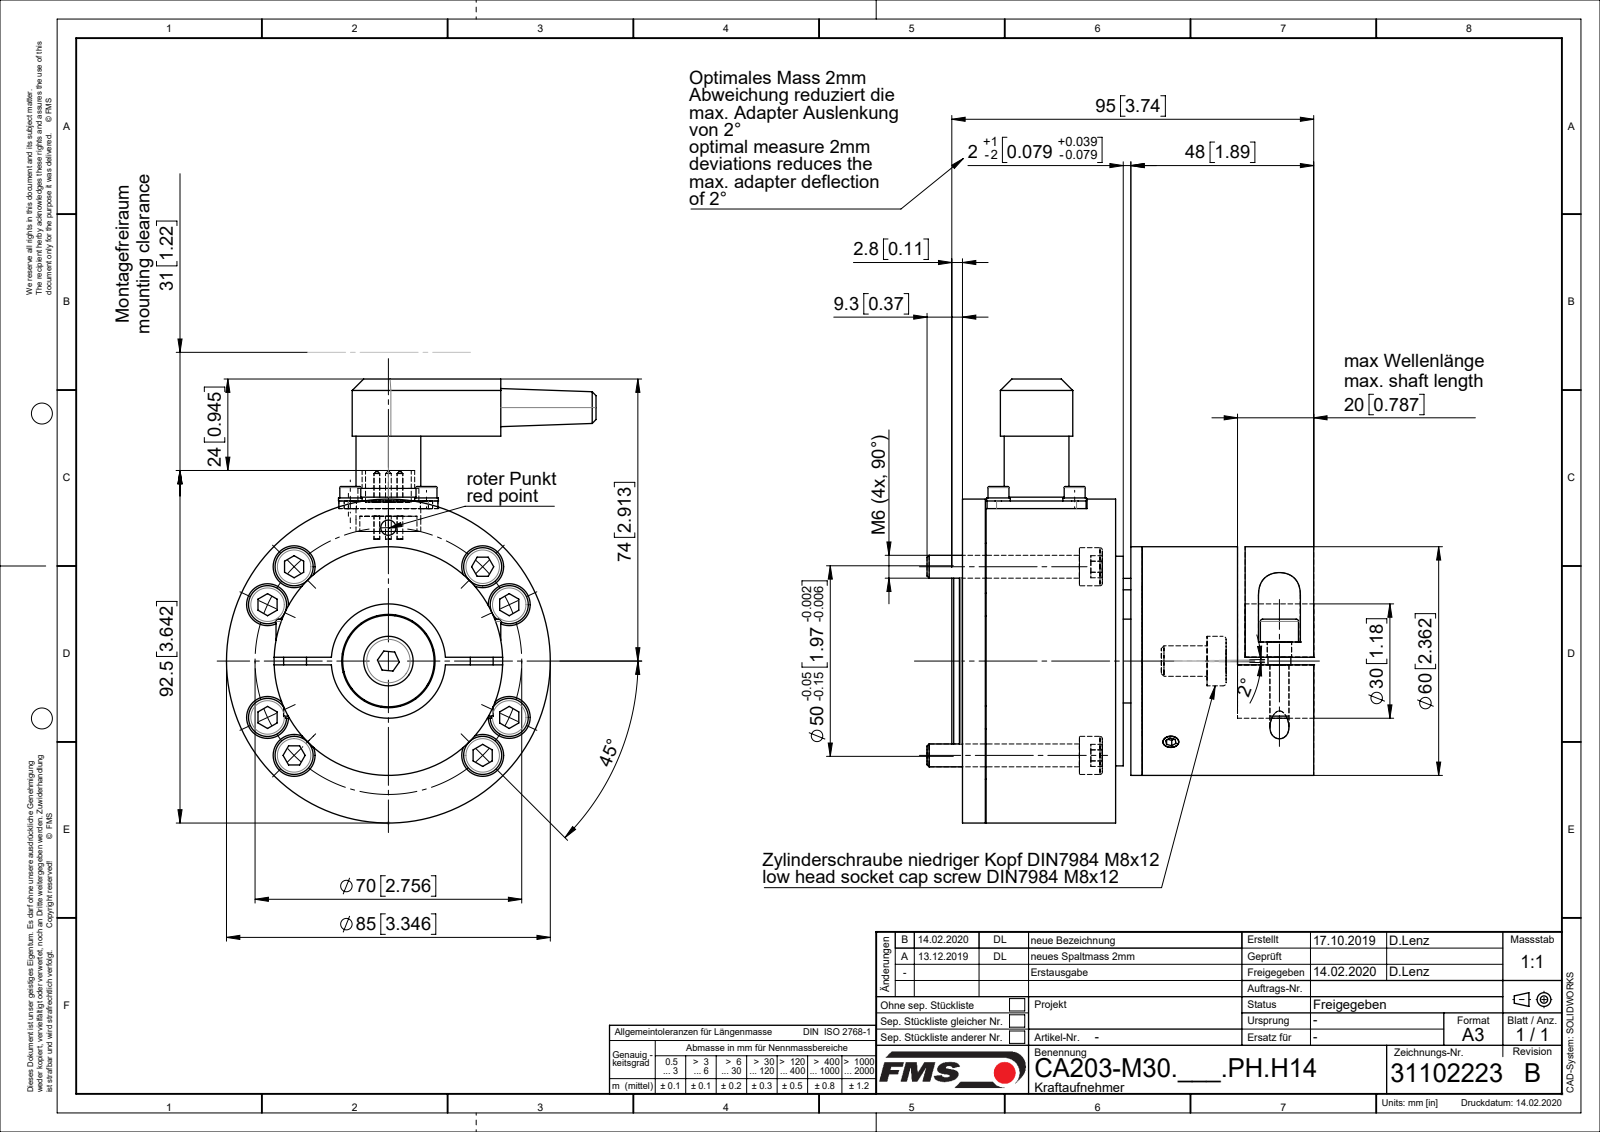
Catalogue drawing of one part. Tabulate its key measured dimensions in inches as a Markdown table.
| quantity | value |
| --- | --- |
| part name | ZEICHNUNG6; C50417_DM30; C0709081; C0612056 (+8 more) |
| STEP written by | Mechanical Desktop 2009 (CONFIG_CONTROL_DESIGN) |
| units | inches |
| bodies | 38 solids, 758 faces (274 planar, 331 cylindrical, 153 other) |
| overall size | 4.587 × 3.976 × 3.819 |
| volume | 18.04 in³ |
| surface area | 171.5 in² |
| round holes (diameter × count) | 0.102 × 8, 0.256 × 8, 0.433 × 8, 0.203 × 6, 0.079 × 5, 0.126 × 4, 0.142 × 4, 0.157 × 4, 0.276 × 4, 0.252 × 2, 0.118 × 1, 0.17 × 1 |
| round bosses / shafts (diameter × count) | 0.236 × 14, 0.394 × 10, 0.118 × 8, 0.059 × 5, 0.244 × 4, 0.217 × 4, 0.197 × 4, 3.346 × 1 |
| partial cylindrical surfaces (radius × count) | 0.157 × 10, 0.098 × 4, 0.197 × 2, 0.217 × 2, 0.374 × 1 |
| main face-to-face distances | 0.453, 0.236, 1.831, 0.079, 1.772, 1.24, 0.059, 0.118, 0.256, 1.949 |
| hole center spacings | 0.976, 0.992, 2.223, 0.787, 1.291, 1.378, 2.013, 0.236 |
